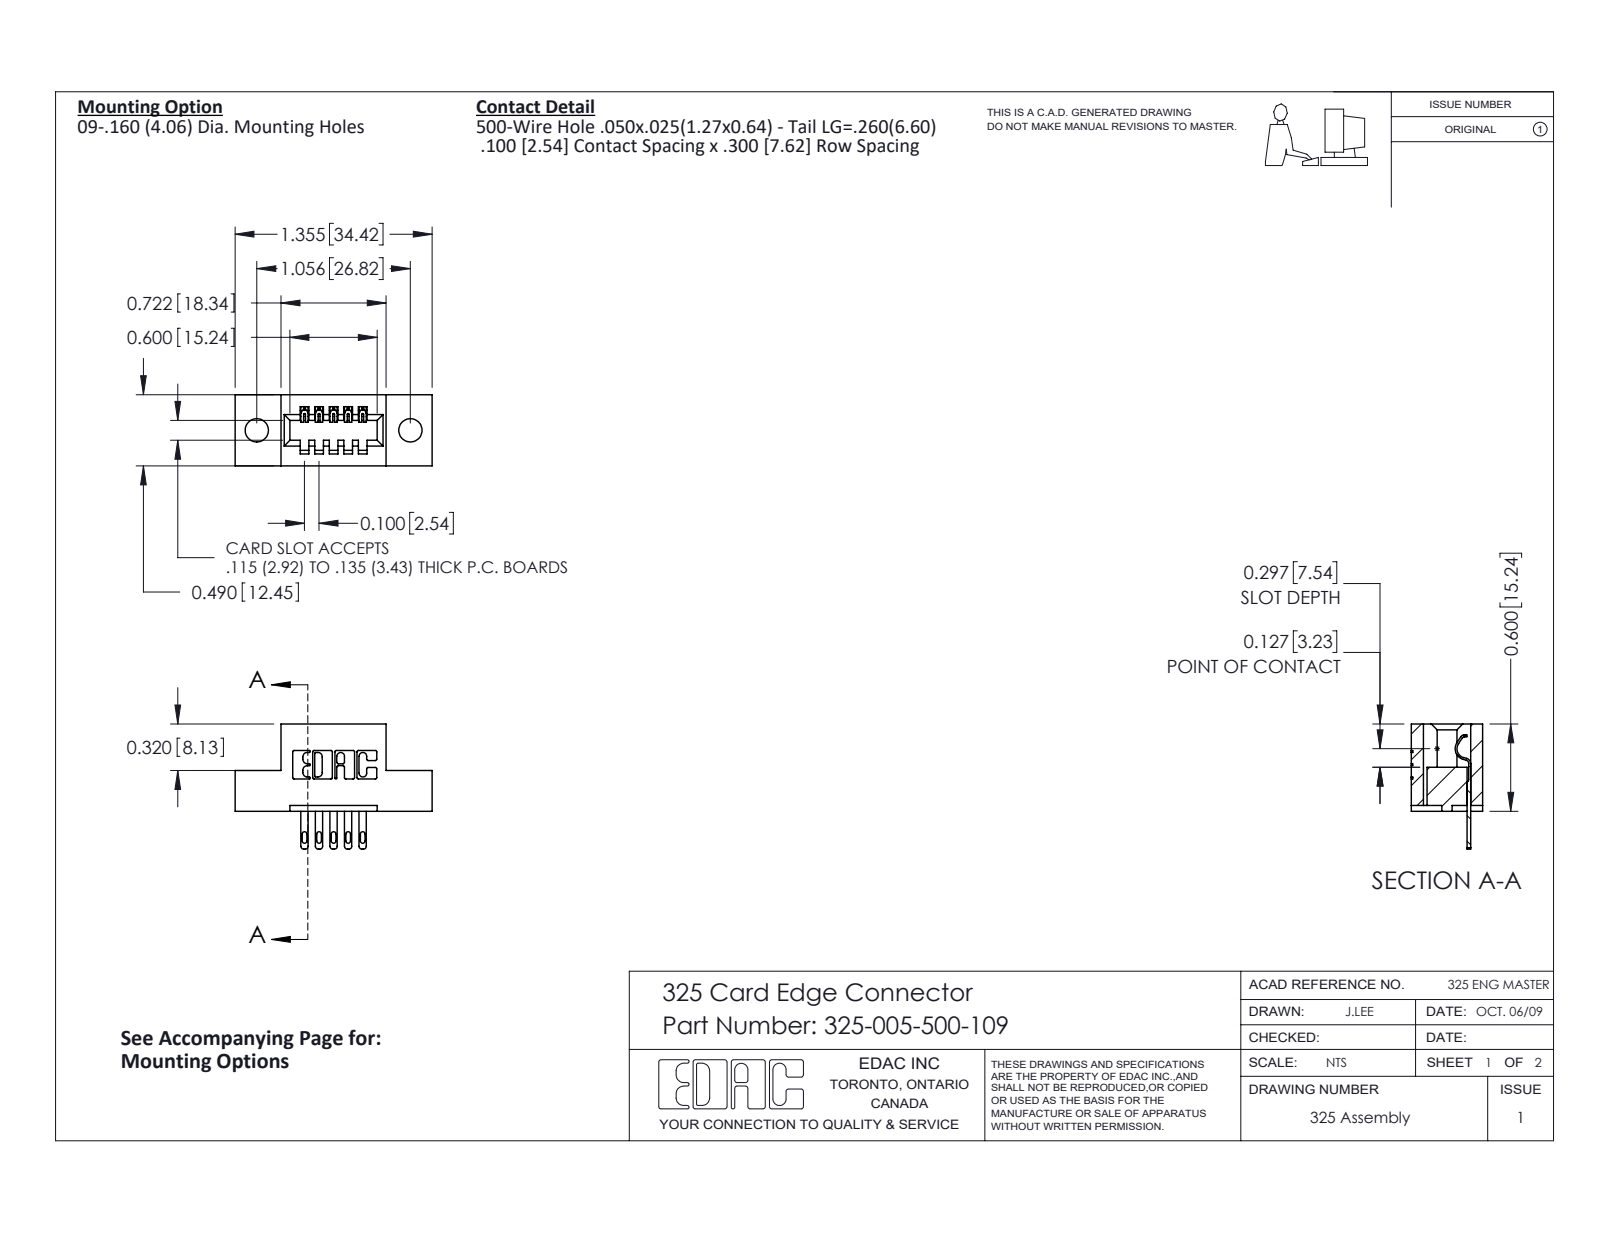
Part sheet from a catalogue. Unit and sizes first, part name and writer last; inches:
Units: inches
Overall size (bounding box): 1.355 × 0.86 × 0.49
Round holes (diameter × count): ⌀0.16 ×2
Partial cylindrical surfaces — rounded edges, fillets, slot ends (radius × count): R0.01 ×22, R0.006 ×10, R0.016 ×10, R0.02 ×10, R0.007 ×6, R0.031 ×6, R0.026 ×3, R0.014 ×1
Main face-to-face distances: 0.1, 0.49, 0.3, 0.04, 0.083, 0.407, 0.2, 0.06, 0.28, 0.317
Hole centre spacings: 1.056
Volume: 0.235 in³ · Surface area: 5.404 in²
Bodies: 6 solids, 384 faces (250 planar, 134 cylindrical, 0 other)
Part name (STEP PRODUCT): 325-005-500-109; 325-292-001_325-293-100; 325 Part_.160 TH
STEP written by: SolidWorks 2016 (CONFIG_CONTROL_DESIGN)
